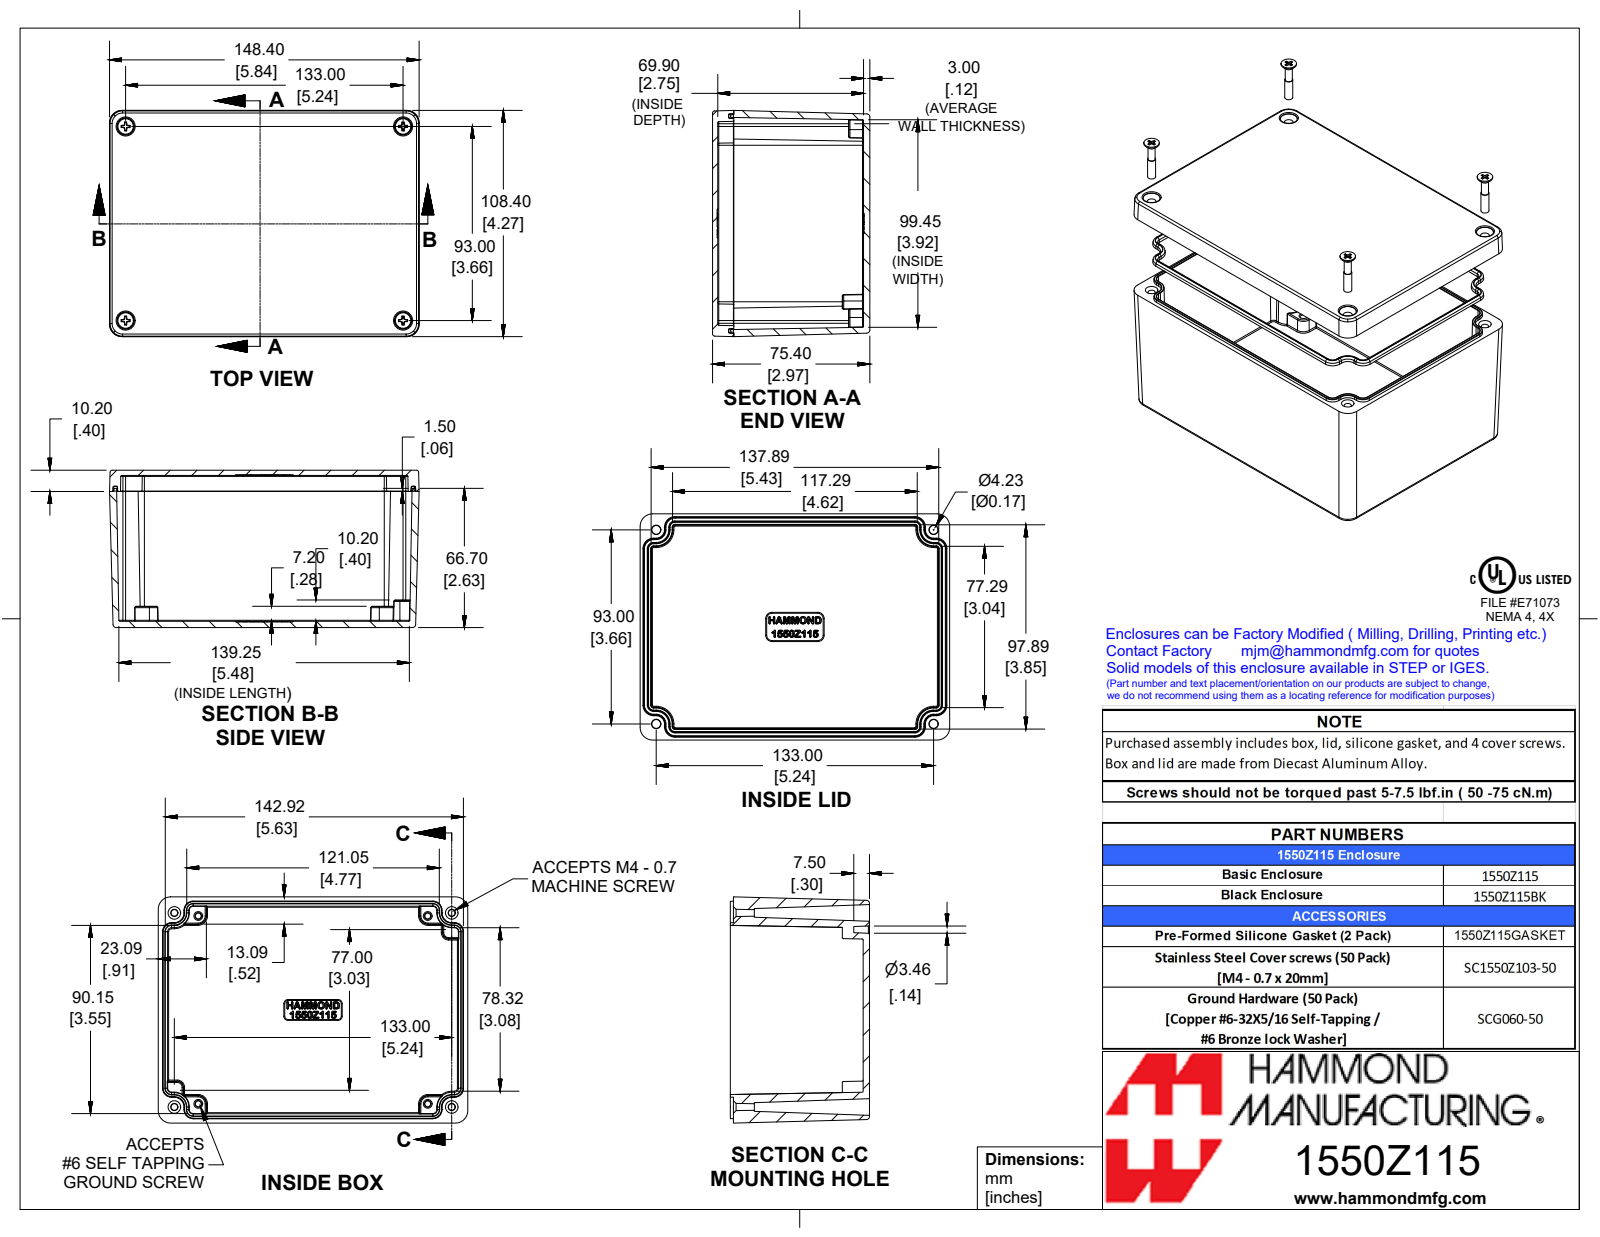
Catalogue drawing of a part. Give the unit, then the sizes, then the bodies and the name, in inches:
Units: inches
Overall size (bounding box): 5.843 × 4.268 × 2.969
Round bosses / shafts (diameter × count): ⌀0.299 ×4, ⌀0.154 ×4, ⌀0.13 ×4
Partial cylindrical surfaces — rounded edges, fillets, slot ends (radius × count): R0.008 ×46, R0.02 ×38, R0.012 ×26, R0.039 ×20, R0.236 ×8, R0.059 ×4
Main face-to-face distances: 2.969, 0.098, 0.118, 2.85, 2.87, 2.752, 0.303, 2.567, 2.449, 0.402
Volume: 13.6 in³ · Surface area: 226.1 in²
Bodies: 7 solids, 1448 faces (393 planar, 262 cylindrical, 793 other)
Part name (STEP PRODUCT): 1550Z115
STEP written by: SolidWorks 2019 (AUTOMOTIVE_DESIGN)
